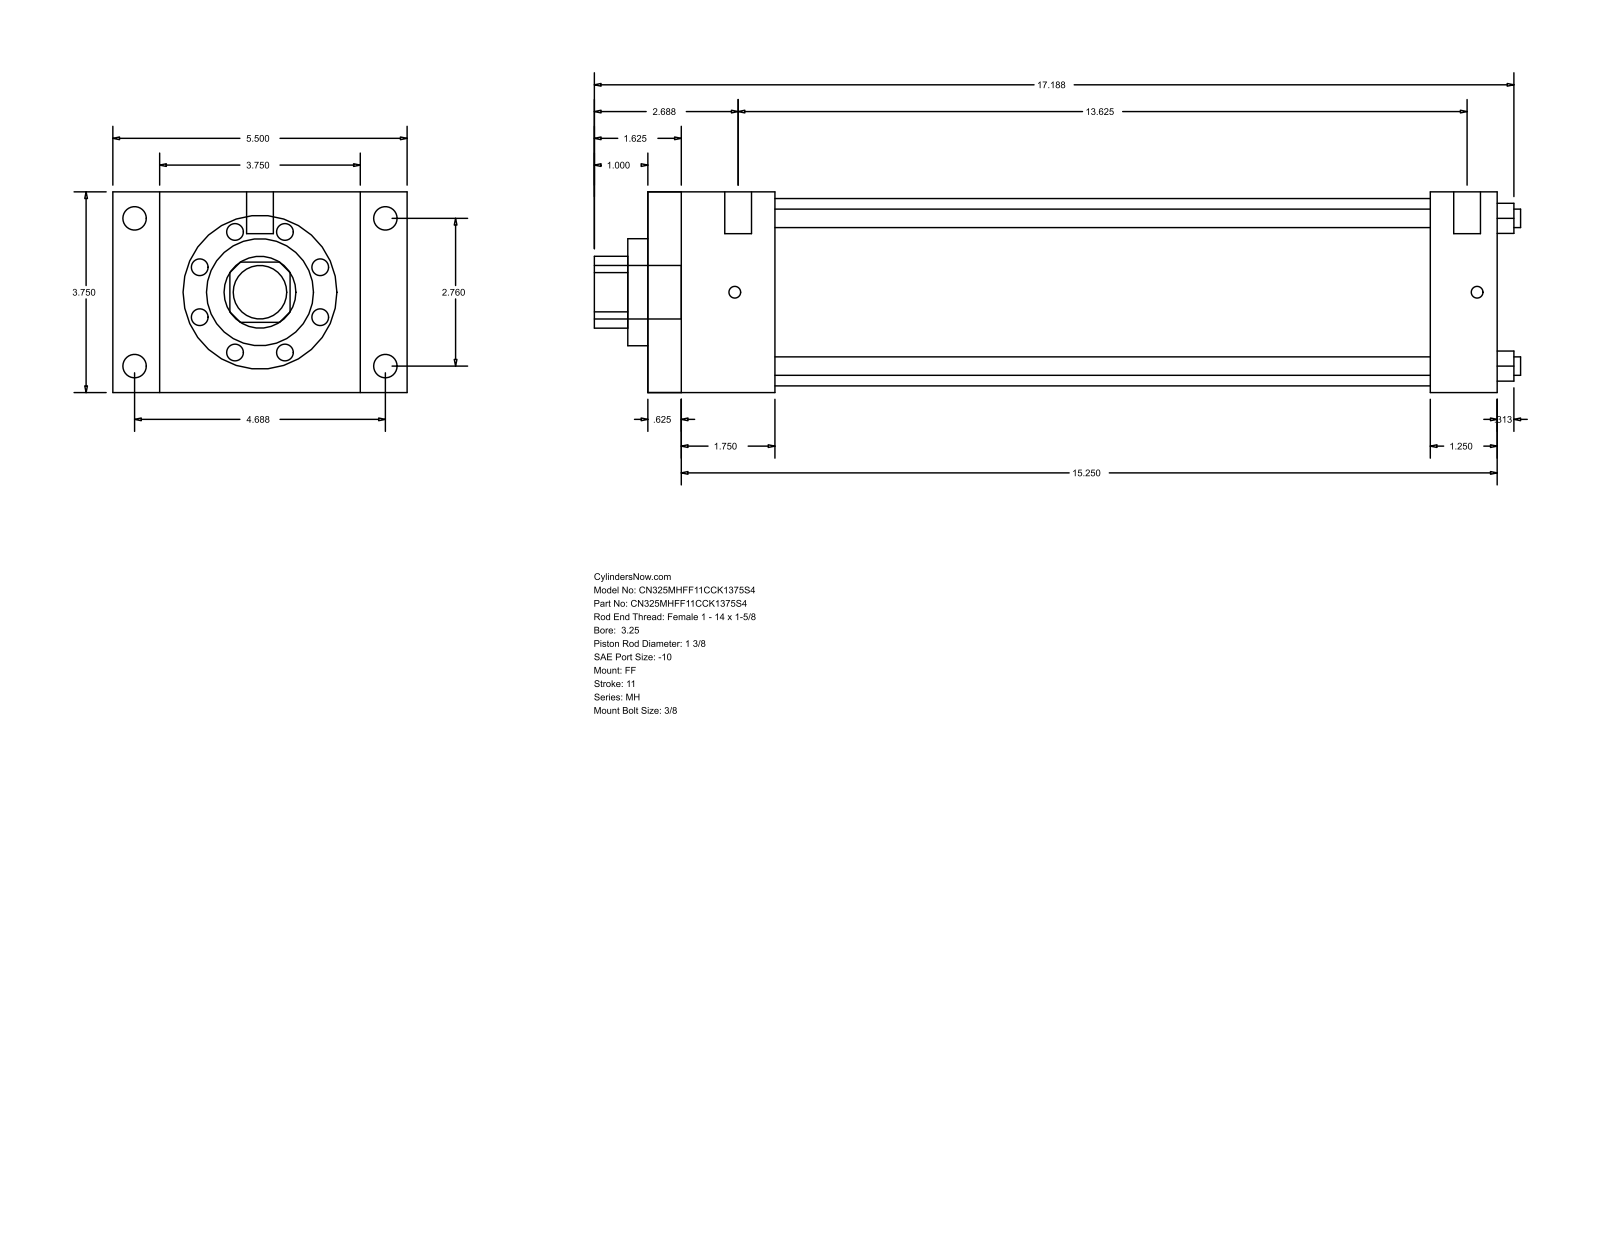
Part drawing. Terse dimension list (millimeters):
name: MH_FF__0325_1.375
written by: GSSL Pune (CONFIG_CONTROL_DESIGN)
unit: mm
bodies: 0 solids, 92 faces (64 planar, 28 cylindrical, 0 other)
size: 439.74 × 139.7 × 95.25
holes: 4× ⌀8.76, 1× ⌀34.92, 1× ⌀50.8, 1× ⌀88.9
bosses: 4× ⌀11.13, 4× ⌀5.56, 2× ⌀12.7, 1× ⌀25.4
rounds: 1× R17.06
face distances: 95.24, 403.22, 15.87, 387.35, 22.23, 117.47, 371.48, 355.61, 31.74, 60.32
hole spacings: 49.57, 70.1, 99.14
